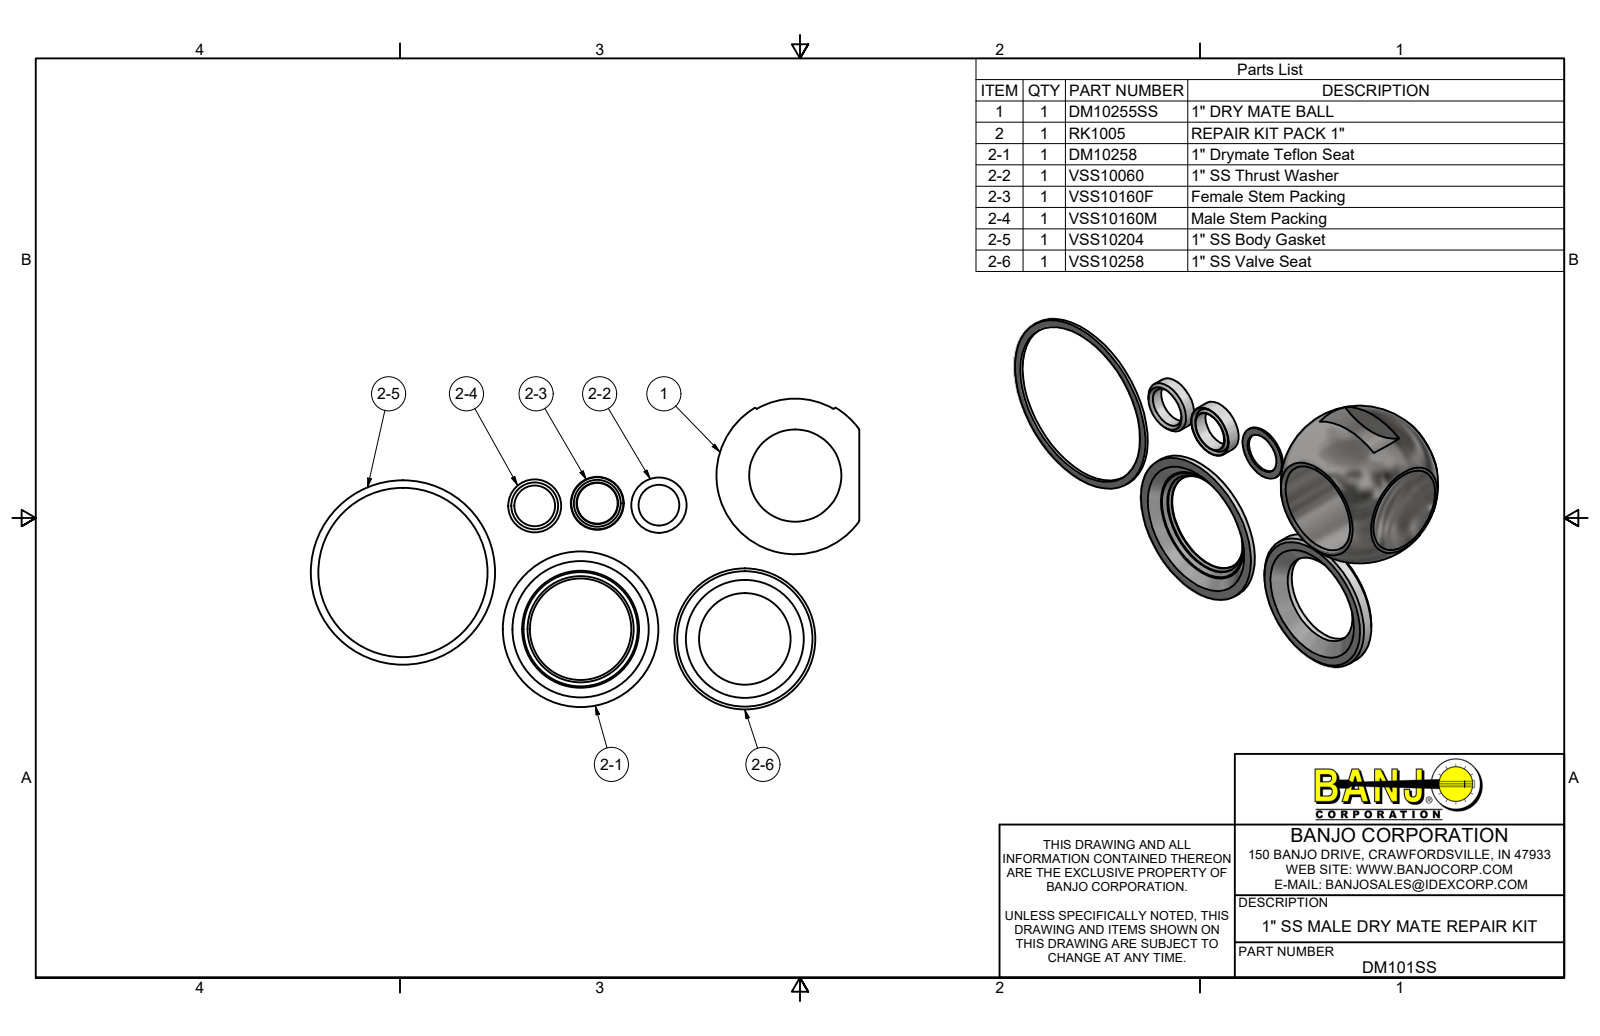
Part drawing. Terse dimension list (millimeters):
name: DM101SS; RK1005; DM10258; VSS10060 (+5 more)
written by: Autodesk Inventor 2019 (AUTOMOTIVE_DESIGN)
unit: mm
bodies: 7 solids, 47 faces (16 planar, 15 cylindrical, 16 other)
size: 148 × 83.8 × 32.9
volume: 23 420 mm³; area: 13 280 mm²
holes: 2× ⌀11, 1× ⌀11, 1× ⌀24.8, 1× ⌀24.9, 1× ⌀27.3, 1× ⌀28.7, 1× ⌀45.7
bosses: 2× ⌀14.3, 1× ⌀49.8, 1× ⌀42, 1× ⌀38, 1× ⌀15
rounds: 1× R19.1
face distances: 4.6, 0.9, 3.7, 4.6, 3.7, 3.1, 2.2, 1.4, 1.5, 0.4
hole spacings: 16.6, 16.9, 33.5, 34.3, 35.5, 37.7, 39.6, 39.8
